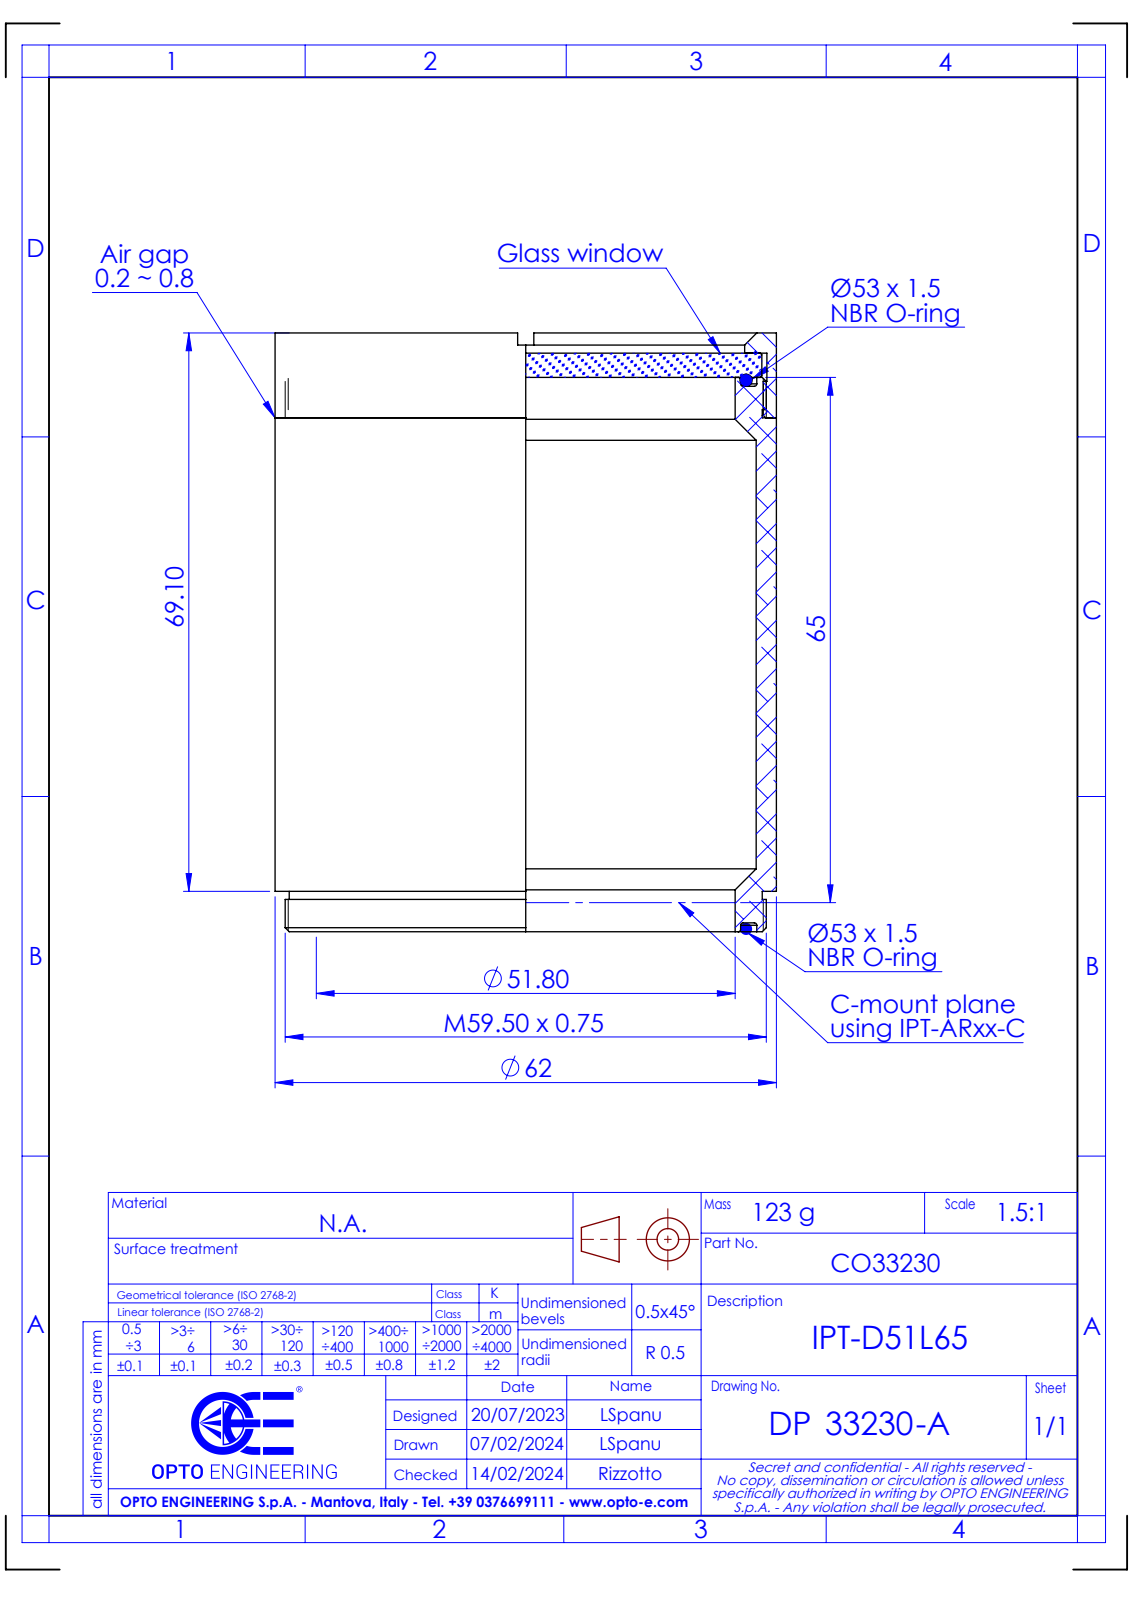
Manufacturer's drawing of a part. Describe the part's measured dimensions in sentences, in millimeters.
The part is named "DP33230-A_IPT-D51L65". Its 3-D file was written by "SolidWorks 2021 (CONFIG_CONTROL_DESIGN)". It is 0 solids with 46 faces: 16 planar, 18 cylindrical and 12 other. Overall it measures 74.1 by 62 by 62 millimeters. Round holes: 1 of diameter 51.8, 1 of diameter 54.15, 1 of diameter 57, 1 of diameter 57.15. Round bosses or shafts: 1 of diameter 62, 1 of diameter 59.5, 1 of diameter 58.5, 1 of diameter 53.15. The main face-to-face distances are 8, 10.5, 2.5, 58.6, 66.6, 69.1, 3.9, 62.5, 70.5, 73.
